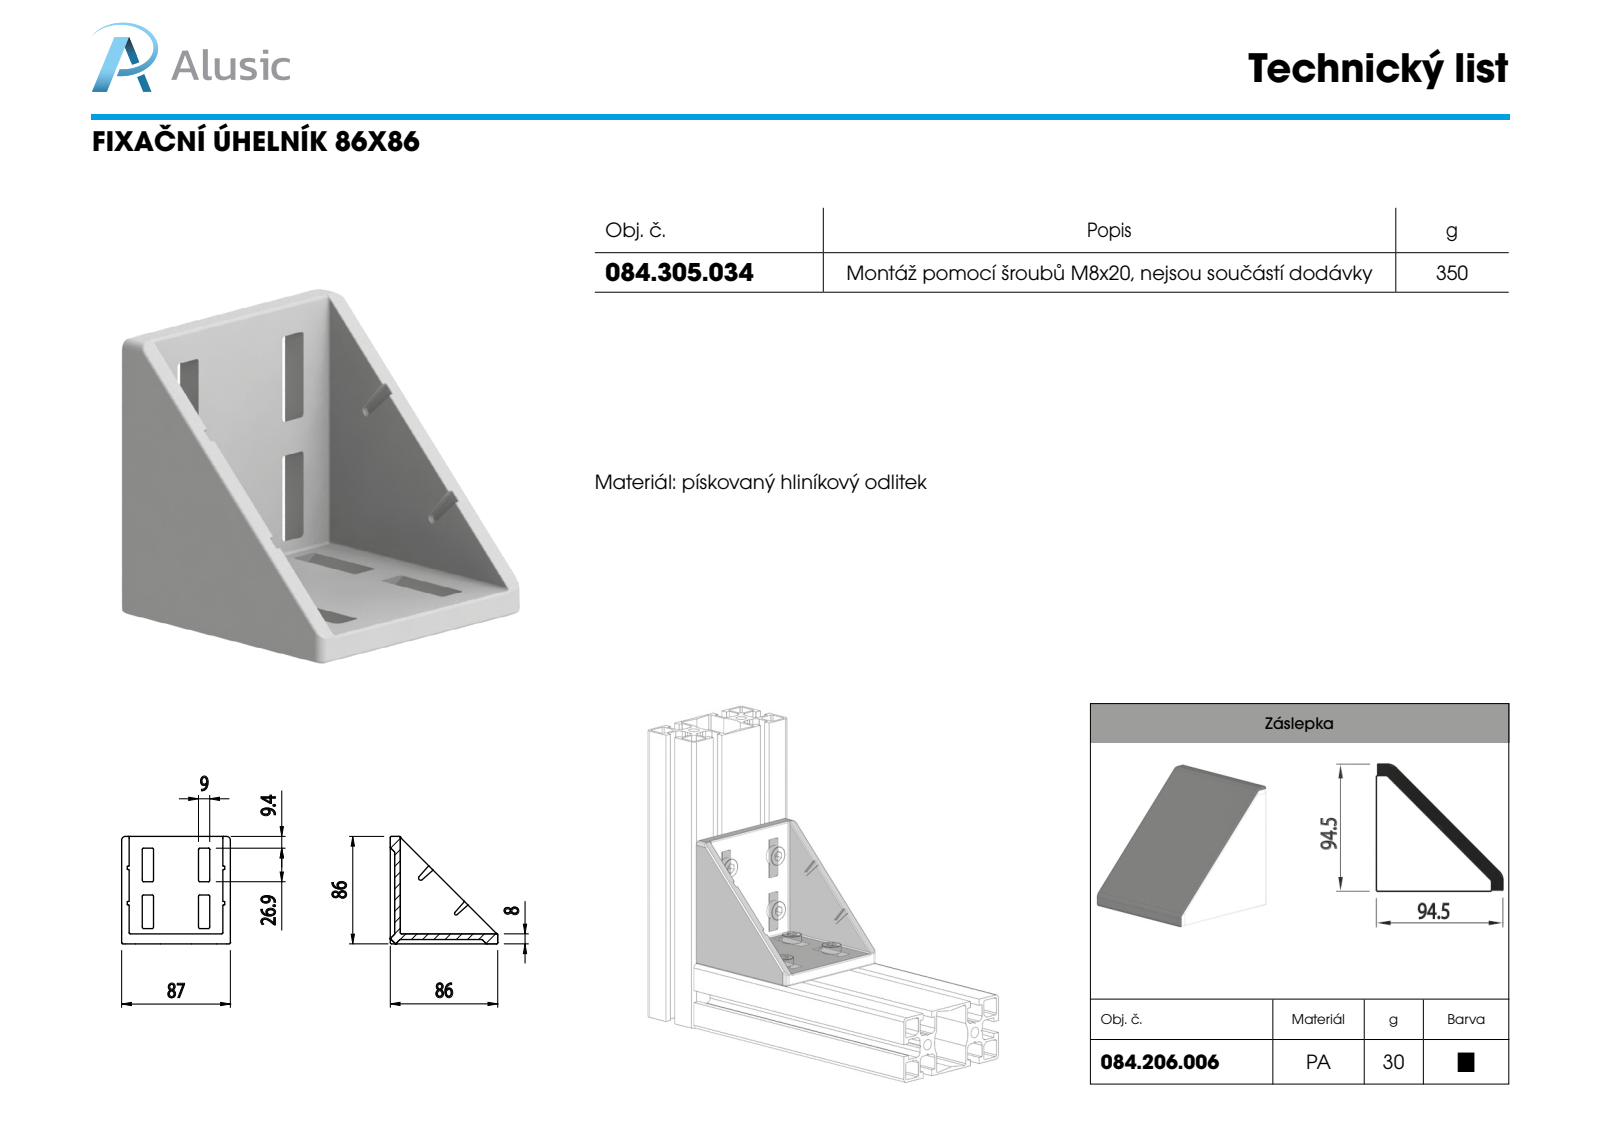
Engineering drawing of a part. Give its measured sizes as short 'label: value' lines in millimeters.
name: 084.305.034
written by: SolidWorks 2012 (CONFIG_CONTROL_DESIGN)
unit: mm
bodies: 1 solid, 722 faces (150 planar, 296 cylindrical, 276 other)
size: 87 × 86 × 86
volume: 106 685 mm³; area: 48 254 mm²
bosses: 12× ⌀4
rounds: 151× R0.5, 54× R1, 4× R3, 2× R1.25
face distances: 4.5, 6, 81, 87, 3.5, 8, 75, 45, 70.5, 25.5
